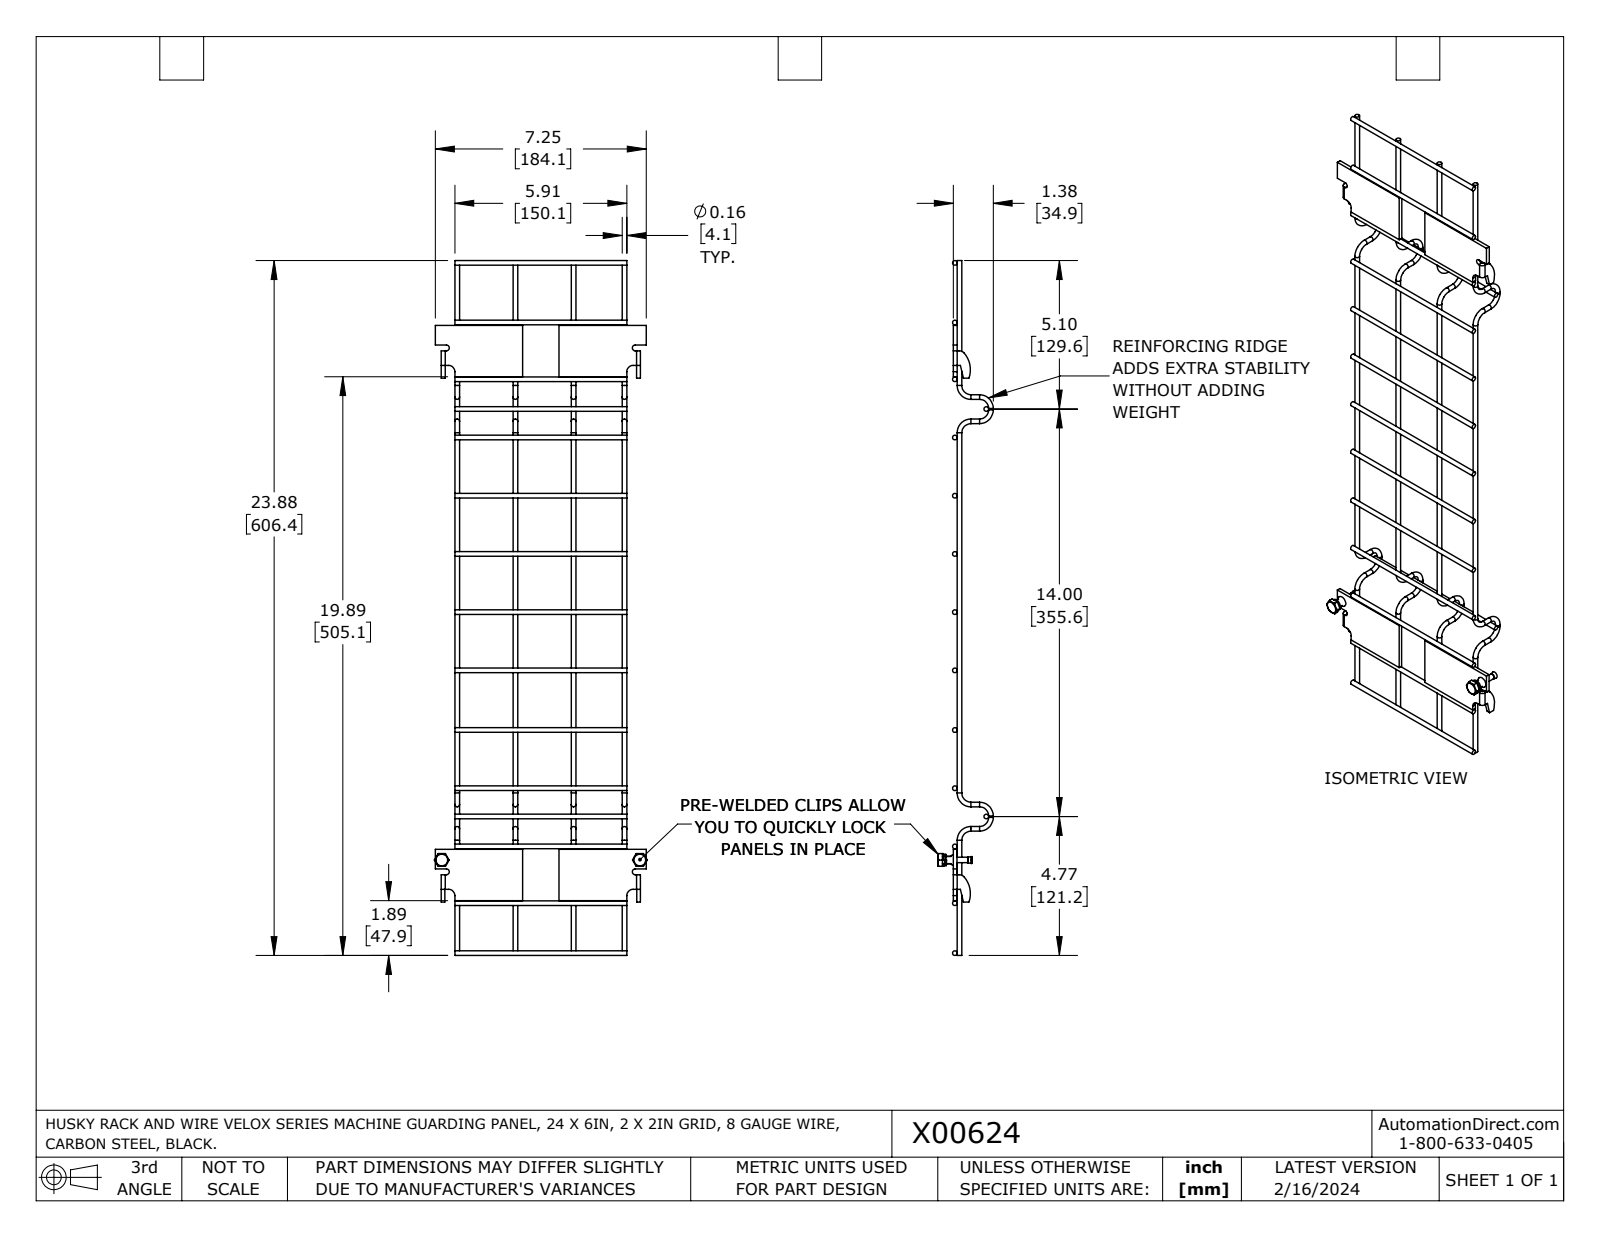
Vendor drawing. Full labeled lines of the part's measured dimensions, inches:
Part name (STEP PRODUCT): X00624
STEP written by: SolidWorks 2023 (AUTOMOTIVE_DESIGN)
Units: inches
Bodies: 27 solids, 261 faces (118 planar, 87 cylindrical, 56 other)
Overall size (bounding box): 23.875 × 7.3 × 1.863
Volume: 6.721 in³ · Surface area: 149.5 in²
Round holes (diameter × count): ⌀0.201 ×2, ⌀0.25 ×2
Round bosses / shafts (diameter × count): ⌀0.16 ×39, ⌀0.39 ×2, ⌀0.245 ×2, ⌀0.187 ×2
Partial cylindrical surfaces — rounded edges, fillets, slot ends (radius × count): R0.1 ×4, R0.218 ×4, R0.009 ×2, R0.067 ×2, R0.134 ×2, R0.25 ×2, R0.865 ×2
Main face-to-face distances: 0.134, 0.125, 18, 1.765, 2.798, 4.046, 0.467, 6.377, 2.331, 3.579
Hole centre spacings: 6.808
